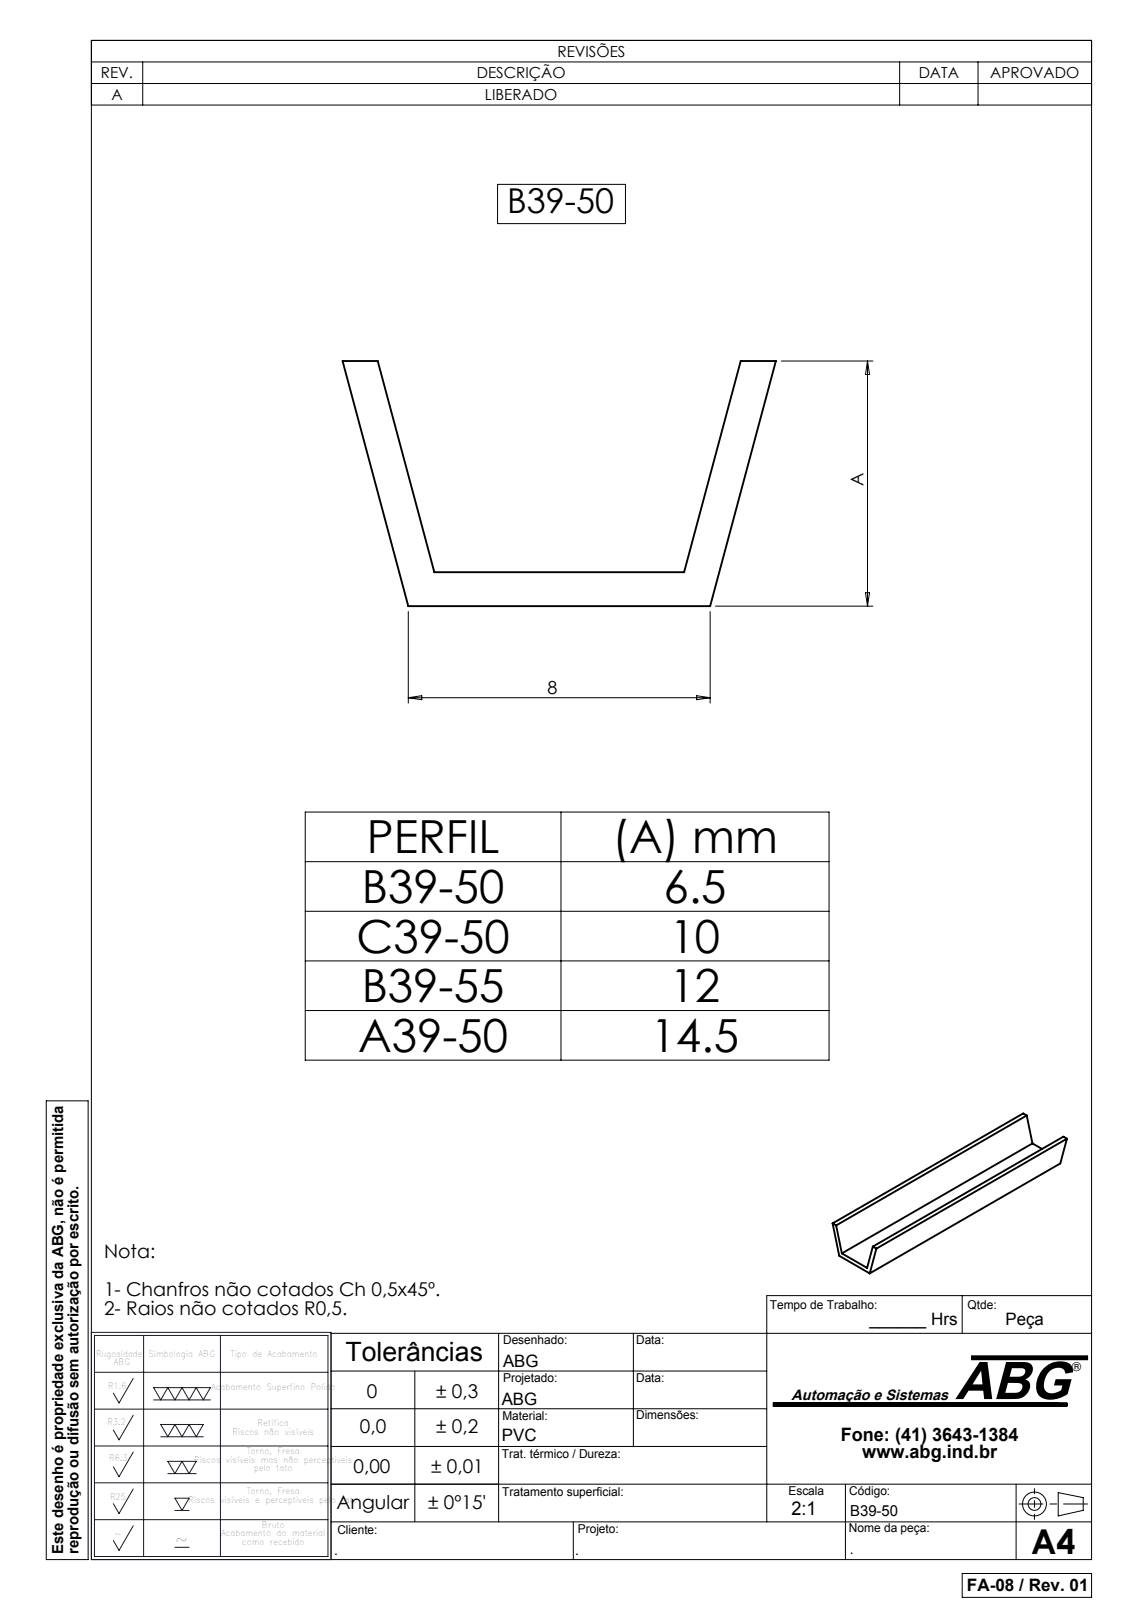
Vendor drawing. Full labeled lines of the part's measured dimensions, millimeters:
Part name (STEP PRODUCT): B39-55
STEP written by: SolidWorks 2007 (CONFIG_CONTROL_DESIGN)
Units: millimetres
Bodies: 1 solid, 10 faces (10 planar, 0 cylindrical, 0 other)
Overall size (bounding box): 50 × 14.43 × 12
Volume: 1 405 mm³ · Surface area: 3 272 mm²
Main face-to-face distances: 0.9, 12, 11.1, 50
